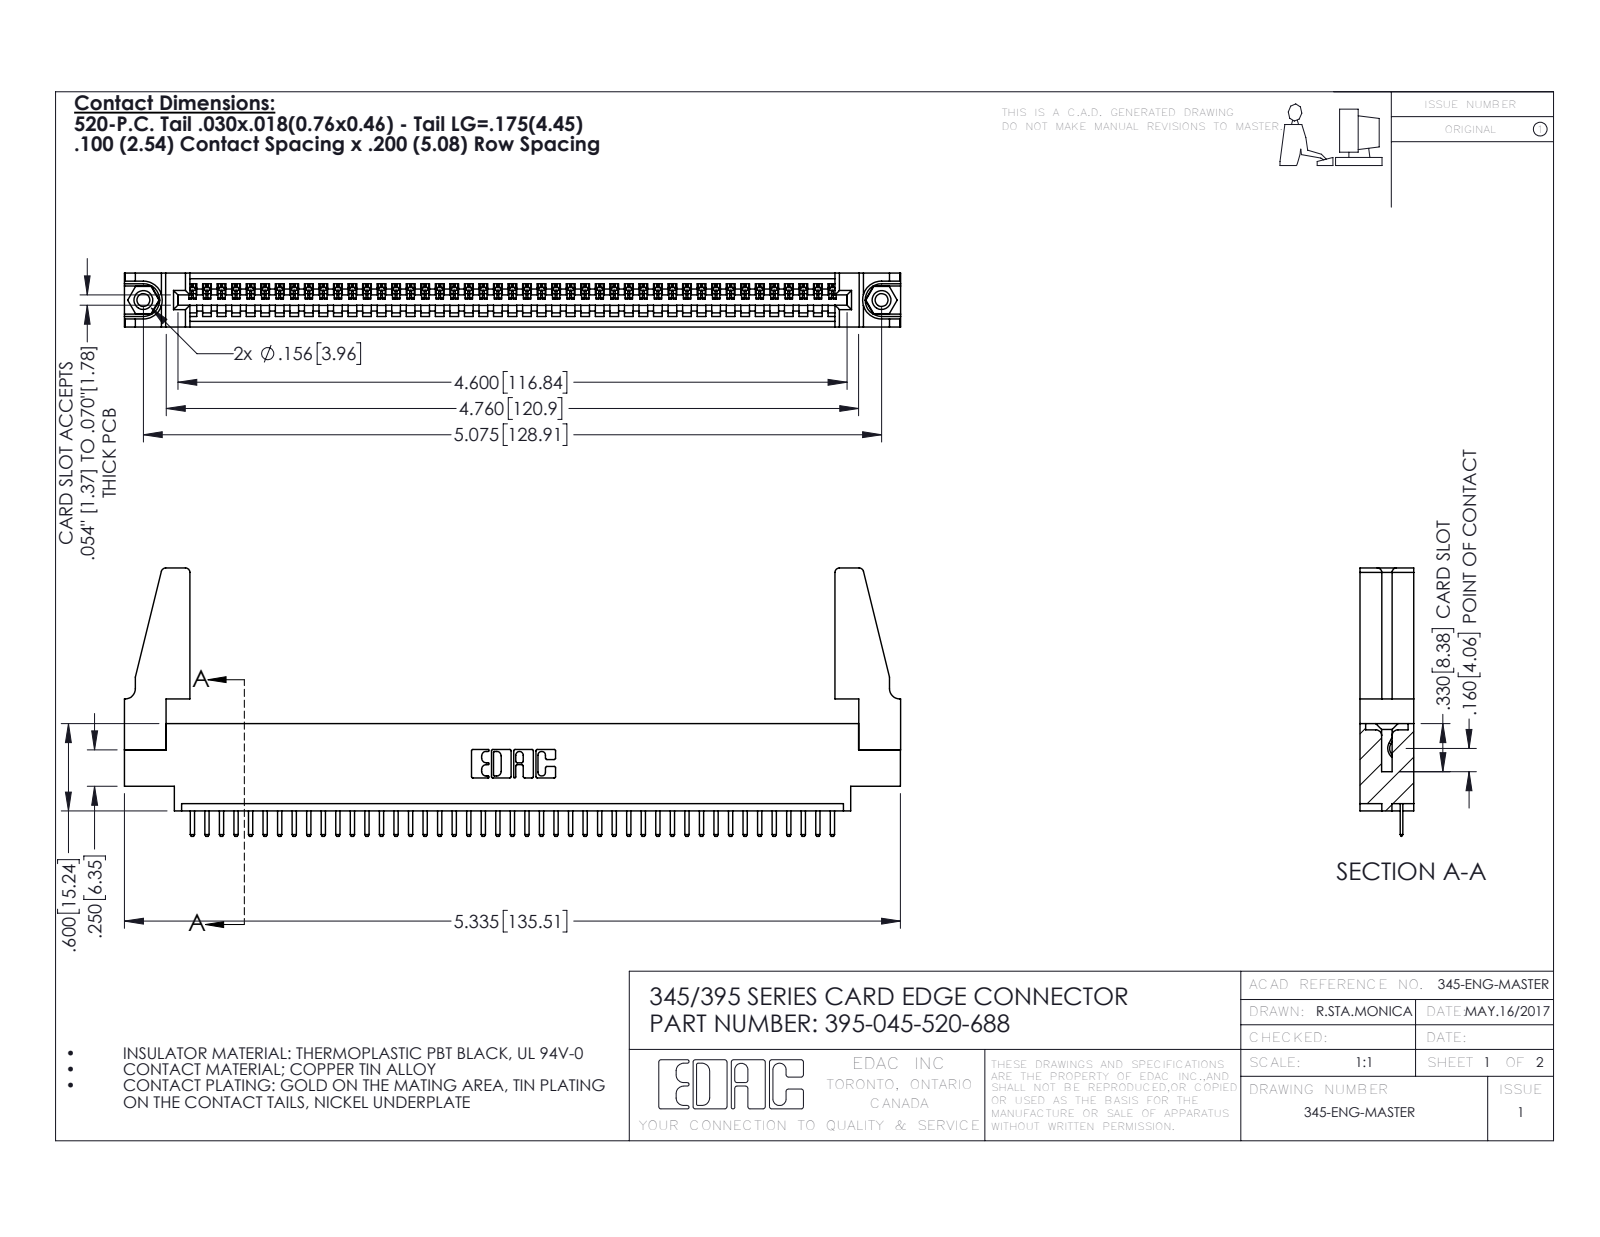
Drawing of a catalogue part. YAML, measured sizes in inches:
part_name: "395-045-520-688; 345-292-001_345-293-120; 345 Part_0.170 Offset - 0.156 Dia-TH; 345-220-078_345-220-088 (+1 more)"
step_written_by: "SolidWorks 2016 (CONFIG_CONTROL_DESIGN)"
units: inches
bodies: {solids: 50, faces: 3044, planar: 2046, cylindrical: 982, other: 16}
overall_size: [5.336, 1.845, 0.37]
volume: 0.971
surface_area: 30.52
round_holes:
  - {diameter: 0.089, count: 2}
  - {diameter: 0.125, count: 2}
  - {diameter: 0.156, count: 2}
  - {diameter: 0.064, count: 1}
round_bosses_or_shafts:
  - {diameter: 0.155, count: 2}
partial_cylinders:
  - {radius: 0.01, count: 92}
  - {radius: 0.006, count: 90}
  - {radius: 0.01, count: 22}
  - {radius: 0.03, count: 8}
  - {radius: 0.007, count: 6}
  - {radius: 0.031, count: 6}
  - {radius: 0.026, count: 3}
  - {radius: 0.031, count: 2}
face_to_face_distances: [0.37, 0.072, 0.298, 0.2, 0.098, 0.272, 0.025, 0.225, 0.072, 0.175]
hole_center_spacings: [0.27, 4.839, 5.075]
